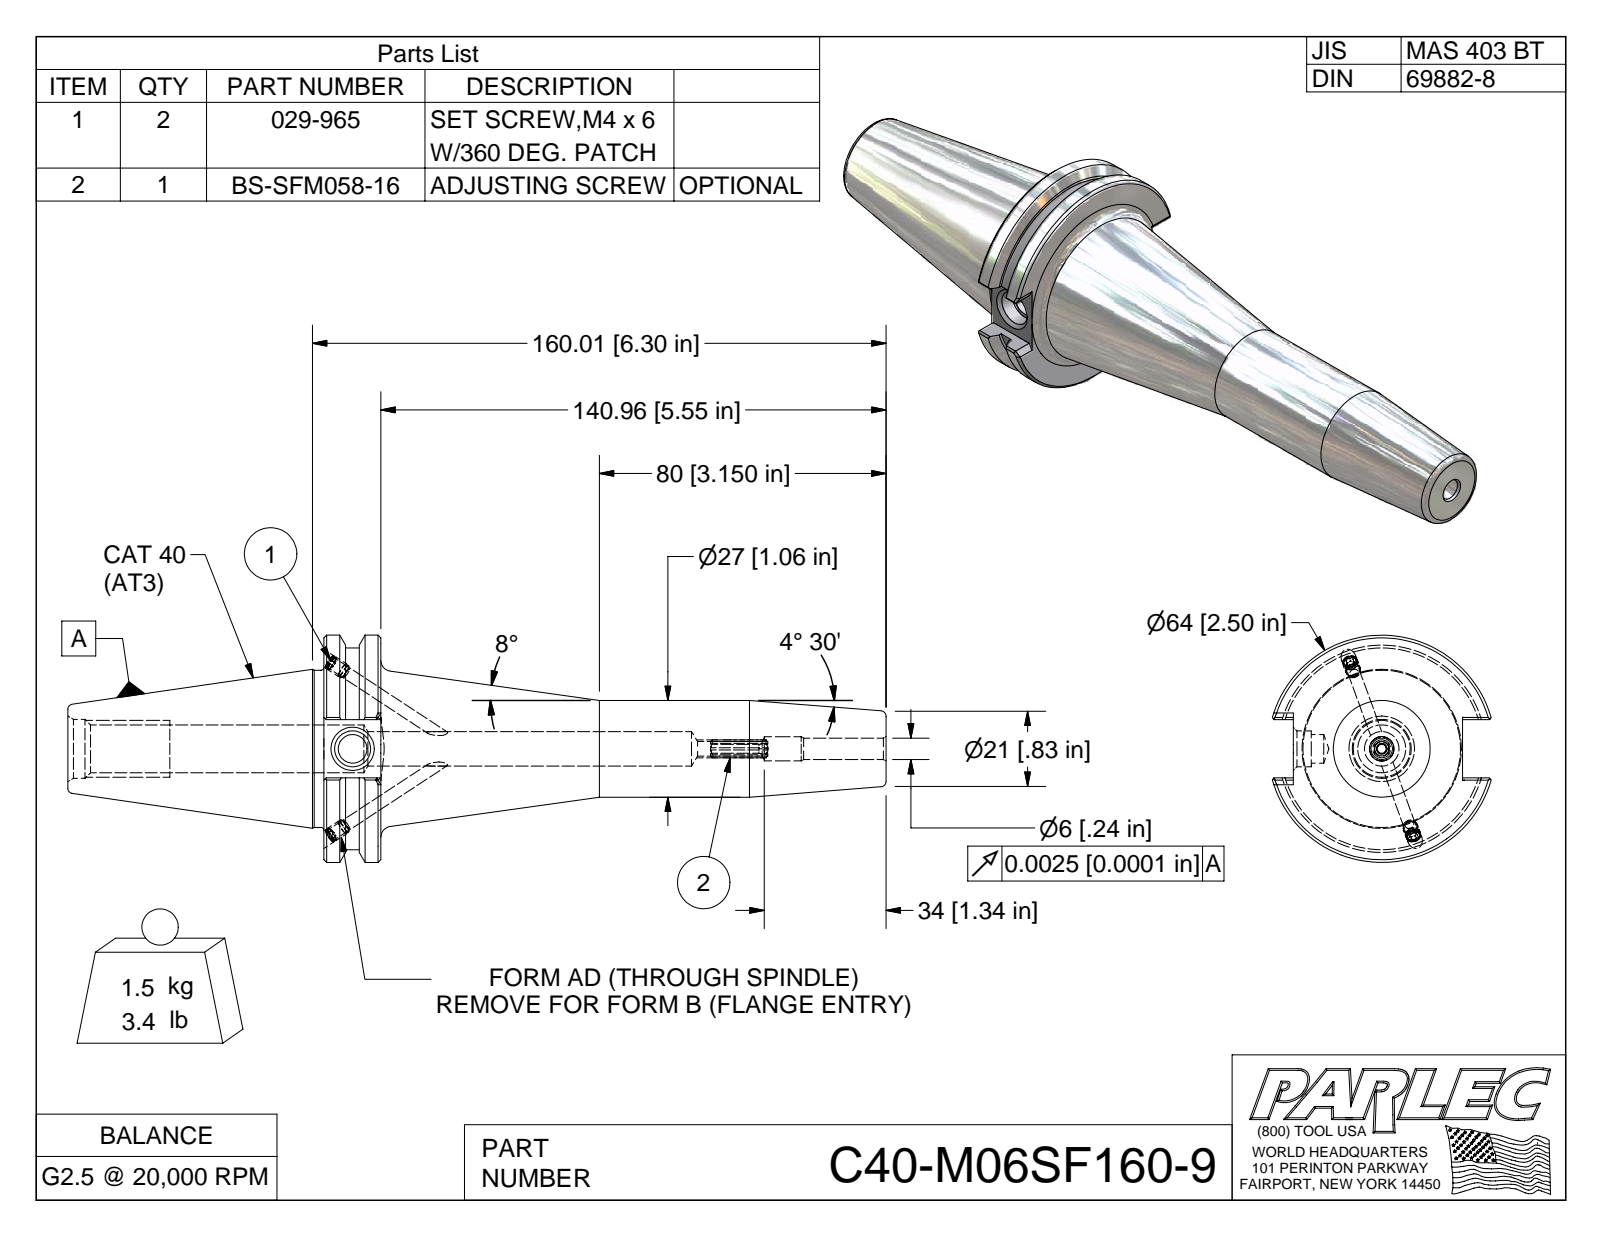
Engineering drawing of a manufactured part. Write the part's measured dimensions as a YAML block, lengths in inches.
part_name: "C40-M06SF160-9; C40BC-M06SF160-9-1; 029-965; BS-SFM058-16"
step_written_by: "Autodesk Inventor 2009 (AUTOMOTIVE_DESIGN)"
units: inches
bodies: {solids: 4, faces: 134, planar: 66, cylindrical: 22, other: 46}
overall_size: [8.987, 2.5, 2.403]
volume: 11.95
surface_area: 57.75
round_holes:
  - {diameter: 0.13, count: 2}
  - {diameter: 0.161, count: 2}
  - {diameter: 0.236, count: 1}
  - {diameter: 0.266, count: 1}
round_bosses_or_shafts:
  - {diameter: 0.165, count: 2}
  - {diameter: 0.157, count: 2}
  - {diameter: 2.5, count: 1}
  - {diameter: 2.219, count: 1}
  - {diameter: 1.73, count: 1}
  - {diameter: 1.063, count: 1}
partial_cylinders:
  - {radius: 0.098, count: 1}
face_to_face_distances: [0.625, 6.175, 5.55, 0.64, 1.86, 2.812, 3.437, 8.987, 3.201, 0.389]
